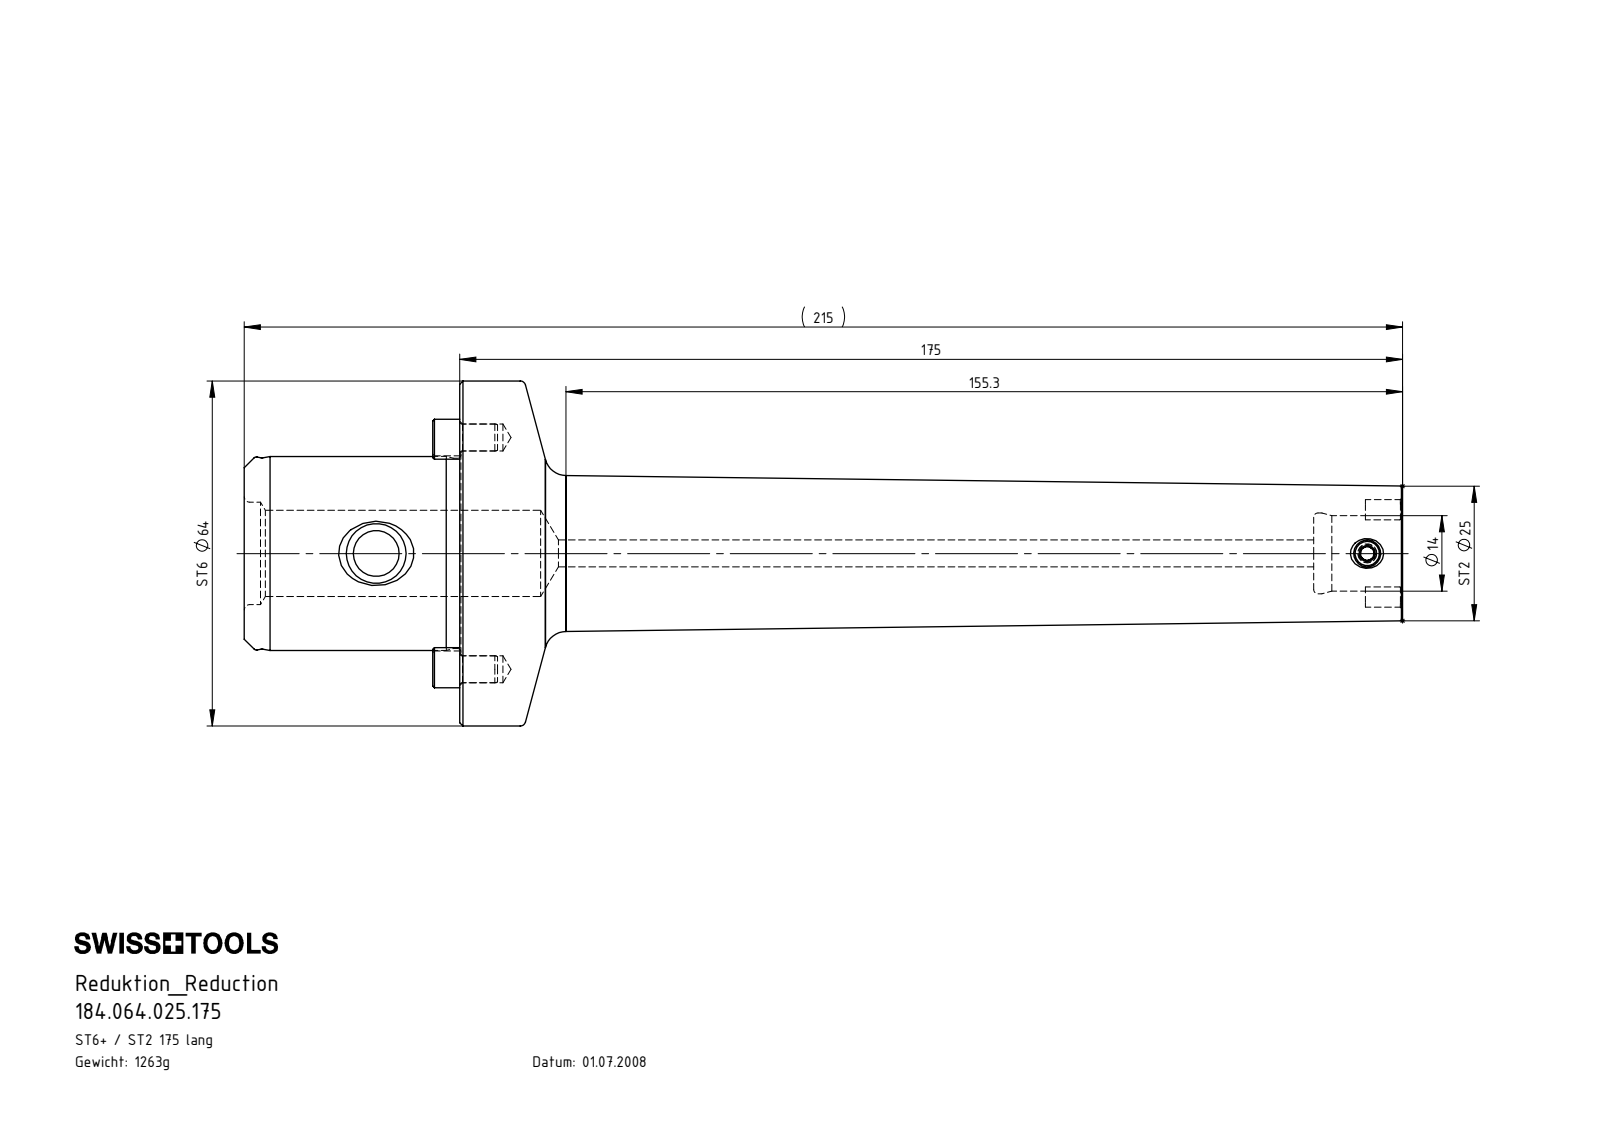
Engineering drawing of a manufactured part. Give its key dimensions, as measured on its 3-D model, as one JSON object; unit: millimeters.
{"part_name": "ST6-ST2.K01.175_B; ST2-ER1.001.006_A; ST6-ER2.001.012_A; 184.064.025.175", "step_written_by": "SolidWorks 2017 (CONFIG_CONTROL_DESIGN)", "units": "millimeters", "bodies": {"solids": 4, "faces": 176, "planar": 32, "cylindrical": 49, "other": 95}, "overall_size": [215, 64, 64], "volume_mm3": 160845, "surface_area_mm2": 33459, "round_holes": [[5, 3], [2.5, 1], [4.5, 1], [8.5, 1], [14, 1], [15, 1], [16, 1], [19, 1]], "round_bosses_or_shafts": [[64, 1], [36, 1], [35.8, 1], [35.3, 1], [5, 1]], "partial_cylinders_radius": [[0.5, 4], [1.8, 2], [5.47, 2], [18.05, 2]], "face_to_face_distances": [40, 215, 175, 198.5, 158.5, 16.5, 35, 5, 163.5, 180], "hole_center_spacings": [21.5, 43, 183.95]}
